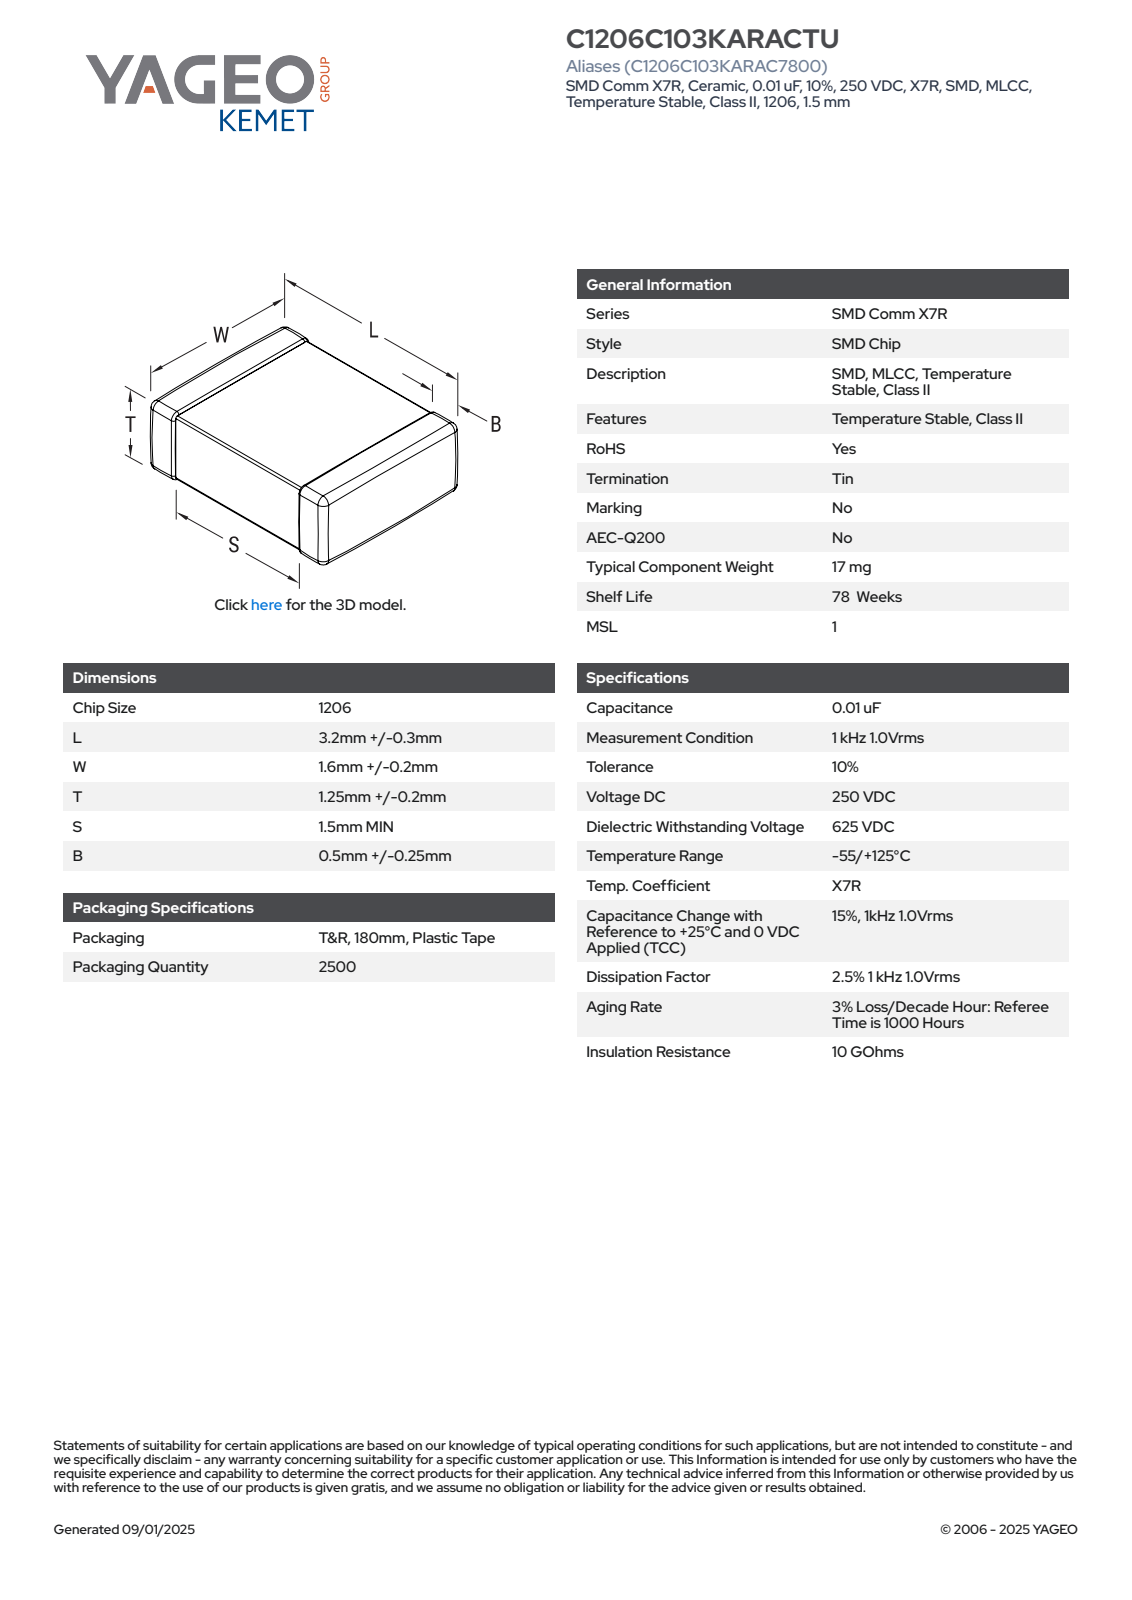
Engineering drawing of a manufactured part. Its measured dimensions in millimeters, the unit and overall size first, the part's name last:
Units: millimetres
Overall size (bounding box): 3.5 × 1.8 × 1.45
Main face-to-face distances: 1.41, 1.76, 1.37, 1.72, 3.5, 1.45, 1.8, 1.42, 1.38, 1.02
Volume: 9 mm³ · Surface area: 28 mm²
Bodies: 4 solids, 125 faces (71 planar, 38 cylindrical, 16 other)
Part name (STEP PRODUCT): CCS_CCSTDNOS_1206_L3.5W1.8T1.45B0.75
STEP written by: SolidWorks 2021 (AUTOMOTIVE_DESIGN)
